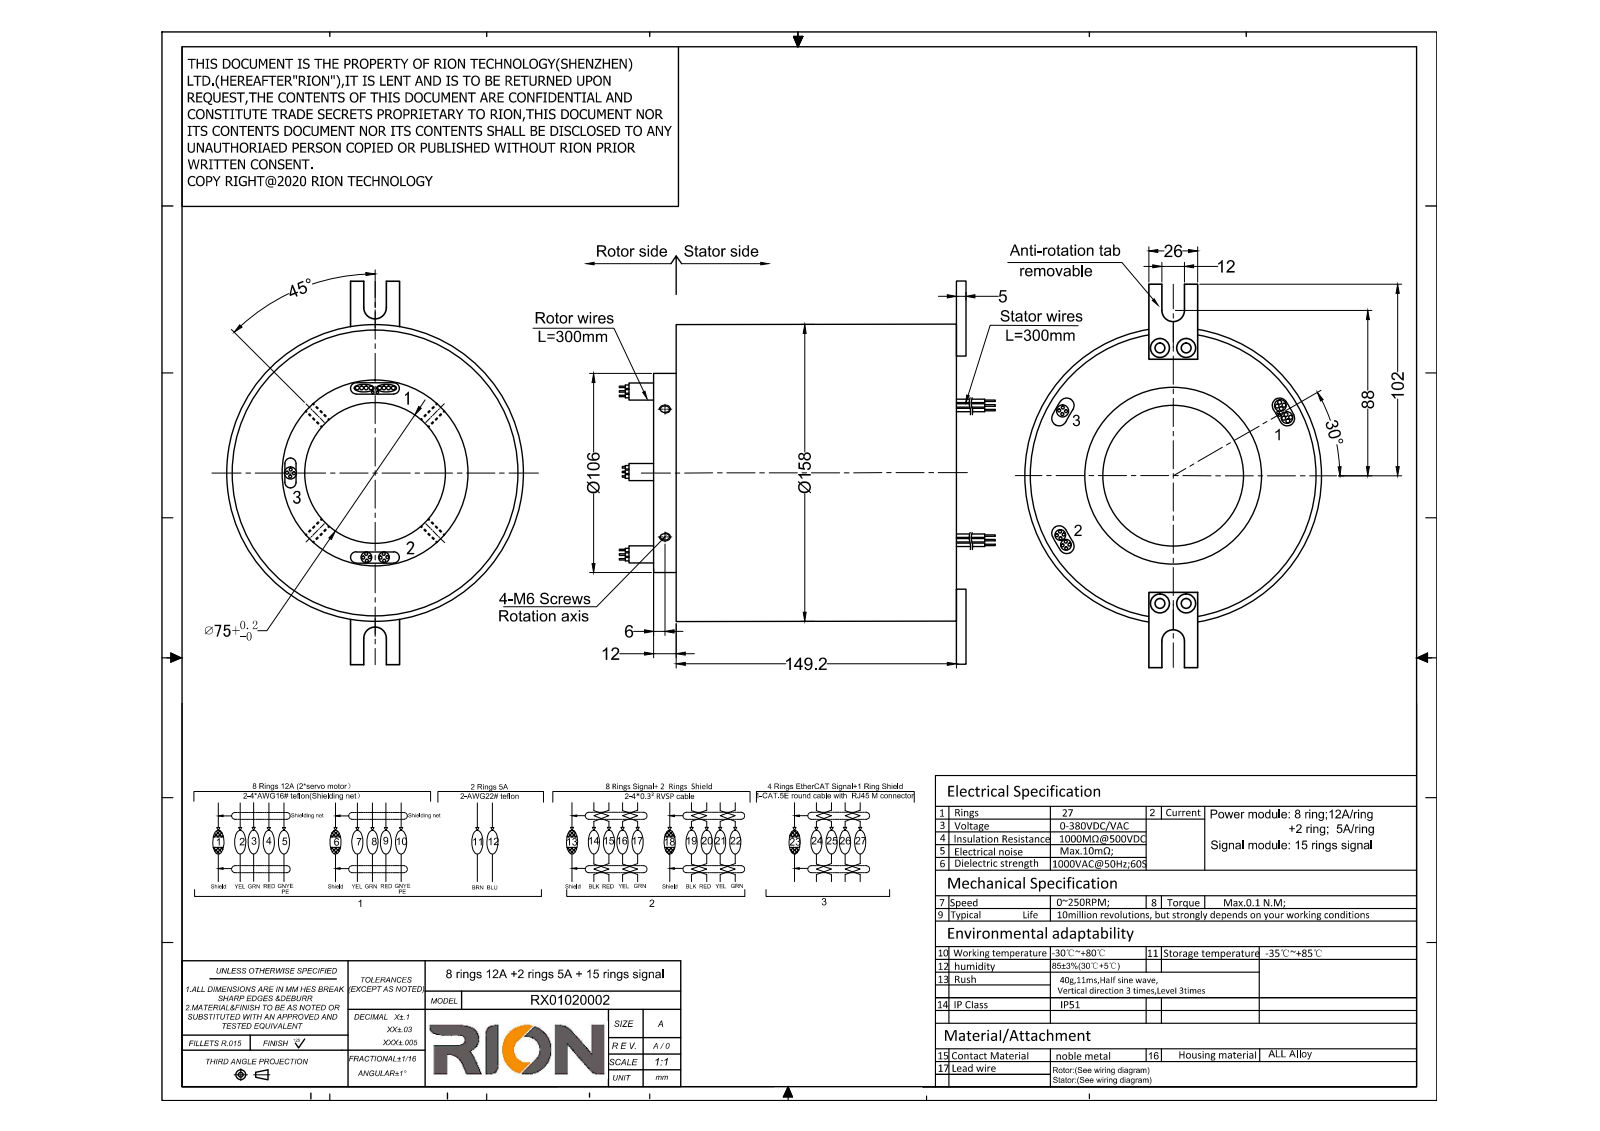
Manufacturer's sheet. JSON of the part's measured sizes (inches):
{"part_name": "RX01020002", "step_written_by": "SolidWorks 2014 (CONFIG_CONTROL_DESIGN)", "units": "inches", "bodies": {"solids": 3, "faces": 176, "planar": 65, "cylindrical": 91, "other": 20}, "overall_size": [9.102, 8.031, 6.22], "volume_in3": 142.5, "surface_area_in2": 259.1, "round_holes": [[0.197, 8], [0.165, 4], [2.953, 1], [3.701, 1], [5.984, 1]], "round_bosses_or_shafts": [[0.228, 4], [0.051, 4], [0.256, 2], [0.241, 2], [6.22, 1], [5.976, 1], [4.173, 1], [3.693, 1]], "partial_cylinders_radius": [[0.118, 6], [0.157, 6], [0.236, 2], [2.518, 1], [2.832, 1]], "face_to_face_distances": [5.874, 0.472, 6.346, 0.197, 6.543, 6.071, 0.039, 6.307, 1.024, 0.276], "hole_center_spacings": [2.691, 0.551, 5.354, 5.383]}
